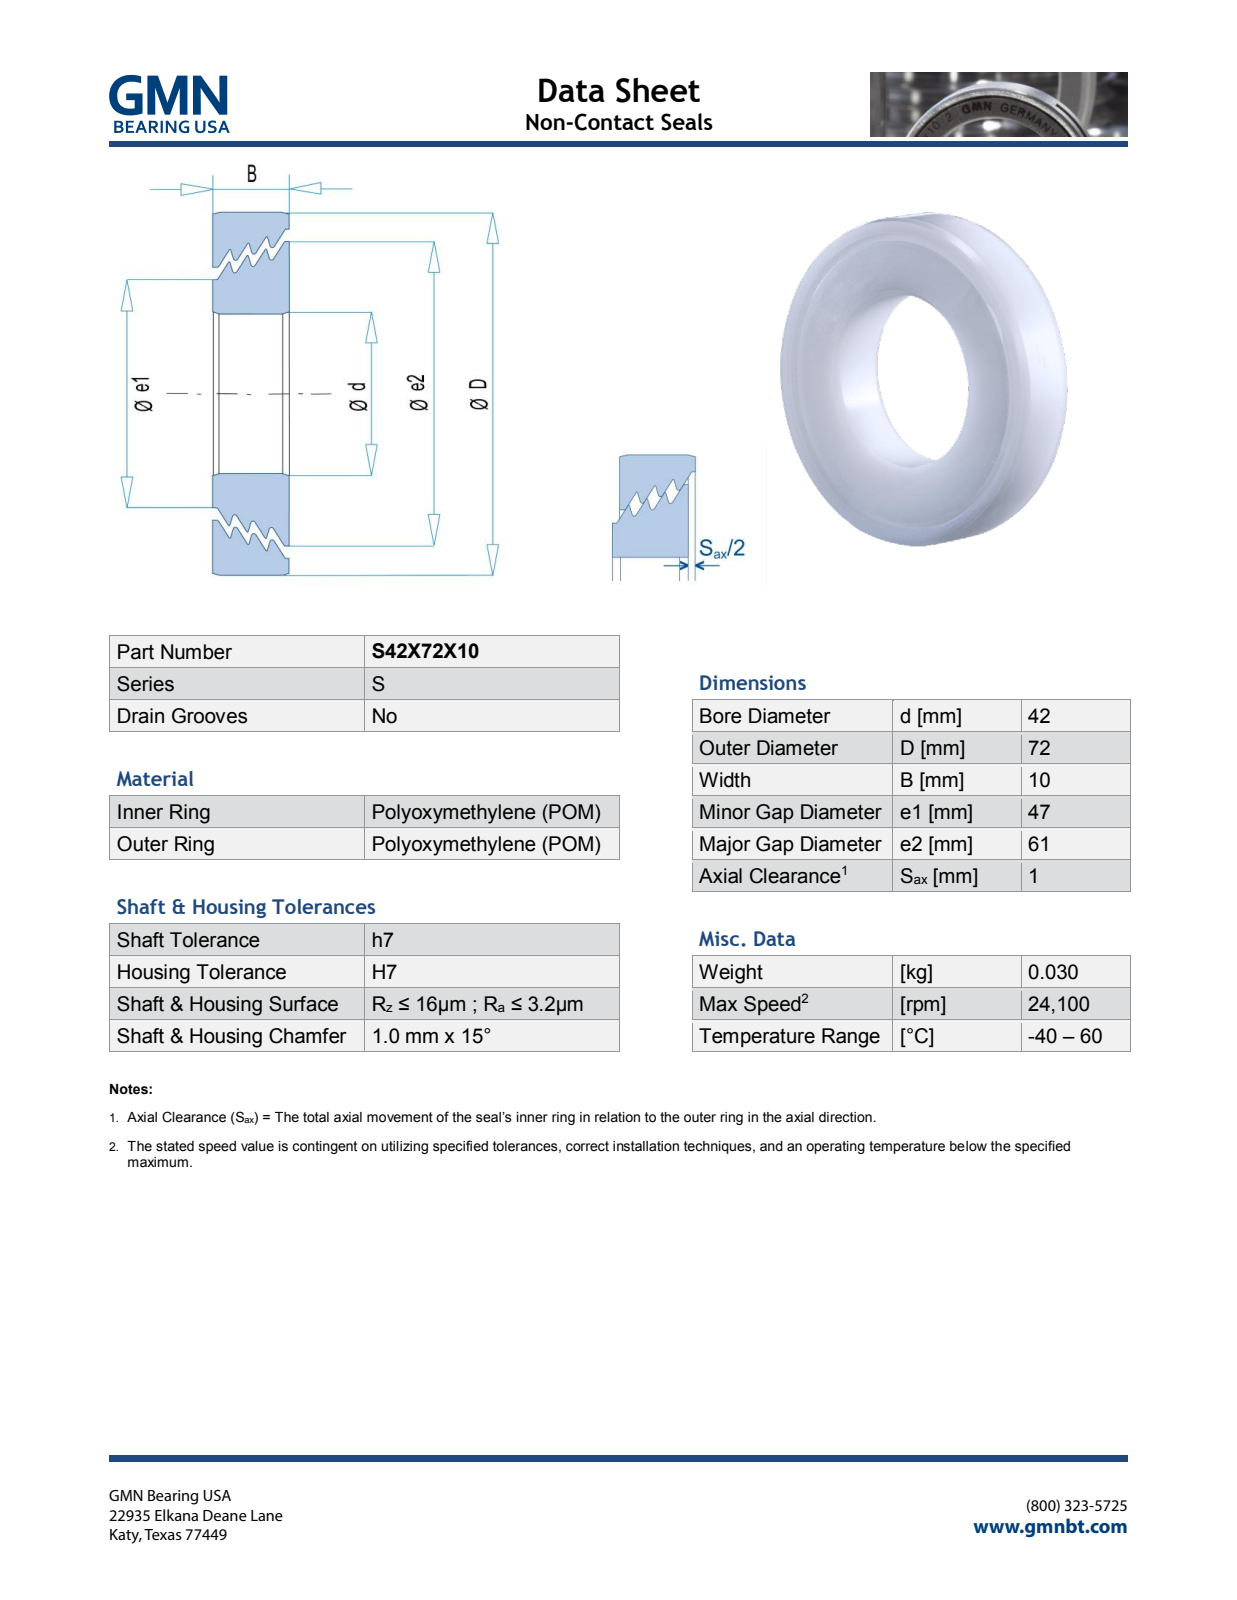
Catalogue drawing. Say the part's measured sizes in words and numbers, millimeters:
The part is named "S42X72X10_PRT". Its 3-D file was written by "PRO/ENGINEER BY PARAMETRIC TECHNOLOGY CORPORATION, 2013150 (AUTOMOTIVE_DESIGN)". It is 2 solids with 575 faces: 495 planar, 12 cylindrical and 68 other. Overall it measures 72 by 72 by 10.07 millimeters. Its volume is 25 363 cubic millimeters and its surface area 15 401 square millimeters. Round holes: 1 of diameter 42, 1 of diameter 48.63, 1 of diameter 62.63. Round bosses or shafts: 1 of diameter 72, 1 of diameter 61, 1 of diameter 47. The main face-to-face distances are 10, 10.07, 0.32, 0.33, 2.58, 2.26, 2.25, 1.94, 2.15, 1.1.
